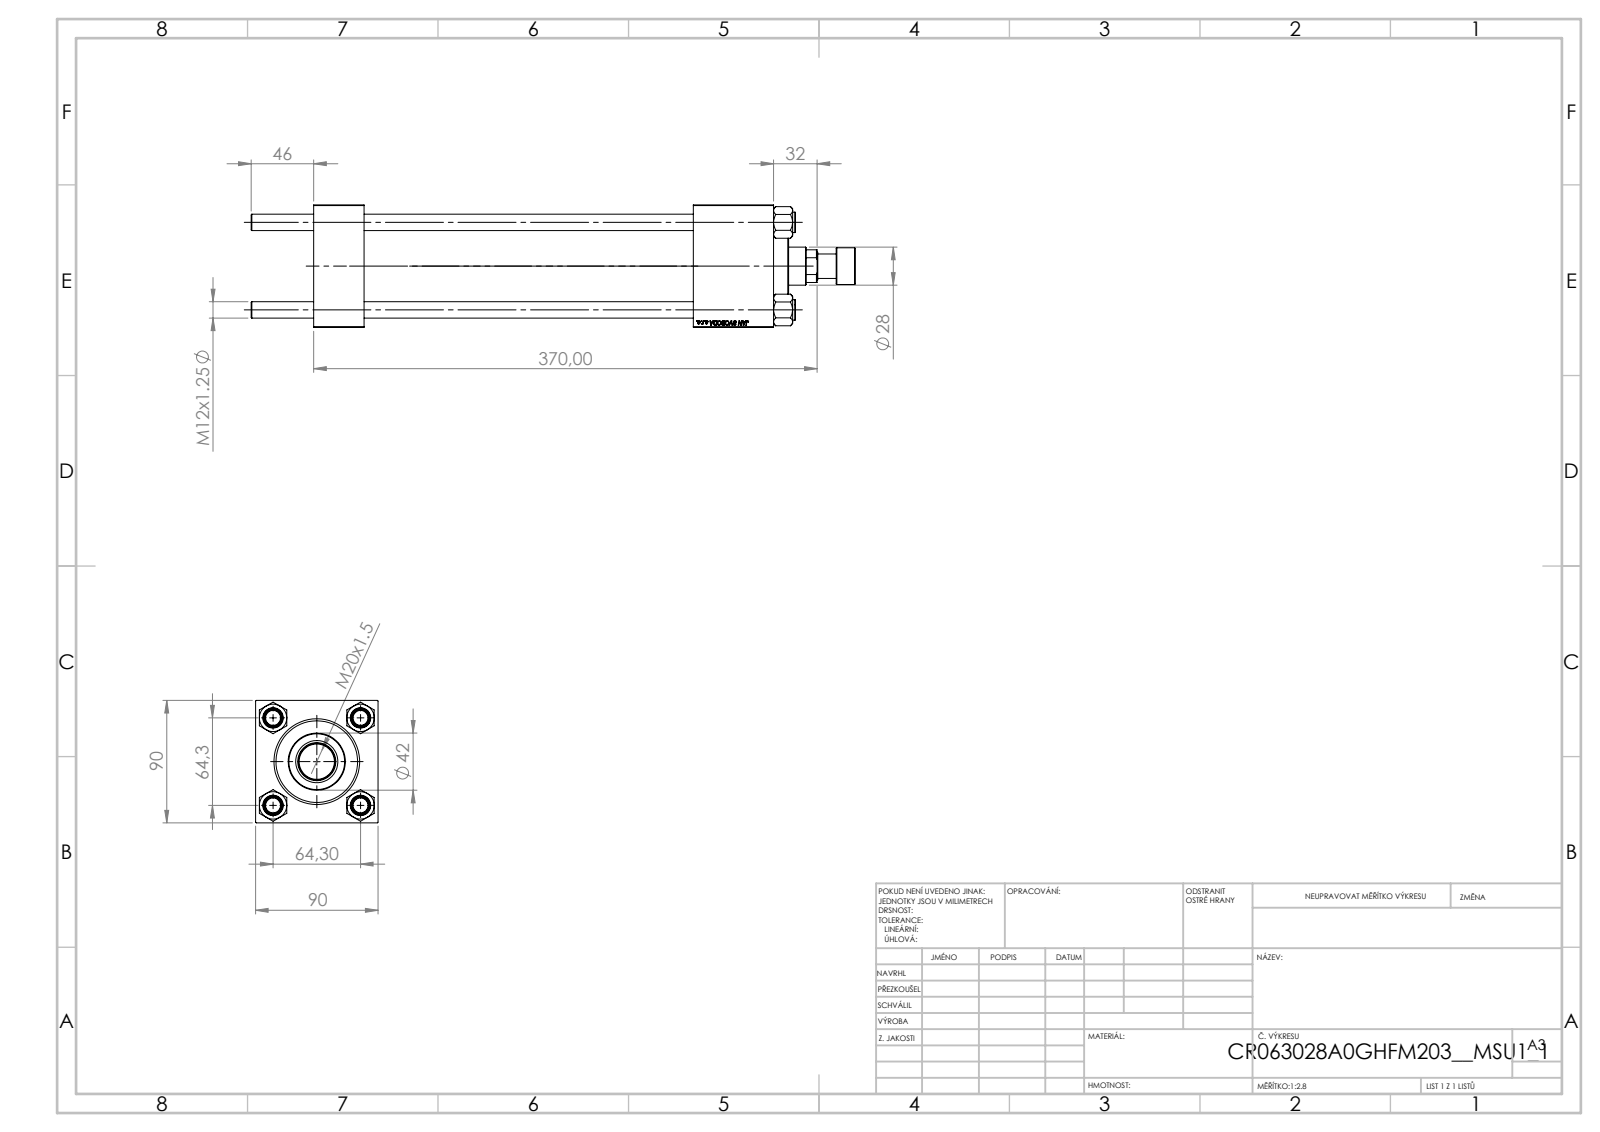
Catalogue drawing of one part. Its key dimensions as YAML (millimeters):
part_name: "V215CR_VCP; NUT_M5; CR025_012_A_0_G_A_G_M_020_+#_##_TYCINKA; V215CR_BODY_A (+2 more)"
step_written_by: "SolidWorks 2019 (CONFIG_CONTROL_DESIGN)"
units: millimeters
bodies: {solids: 12, faces: 1148, planar: 524, cylindrical: 82, other: 542}
overall_size: [444, 90, 90]
volume: 1302000
surface_area: 318102
round_holes:
  - {diameter: 12, count: 4}
  - {diameter: 7, count: 2}
  - {diameter: 20.96, count: 2}
  - {diameter: 30, count: 2}
  - {diameter: 18.5, count: 1}
  - {diameter: 28, count: 1}
  - {diameter: 31, count: 1}
  - {diameter: 50, count: 1}
  - {diameter: 60, count: 1}
  - {diameter: 63, count: 1}
round_bosses_or_shafts:
  - {diameter: 15, count: 4}
  - {diameter: 69, count: 1}
  - {diameter: 42, count: 1}
  - {diameter: 27, count: 1}
  - {diameter: 18, count: 1}
face_to_face_distances: [90, 37, 338, 301, 279, 242, 59, 309.3, 272.3, 30.3]
hole_center_spacings: [45.47, 64.3, 90.93, 280.5]
